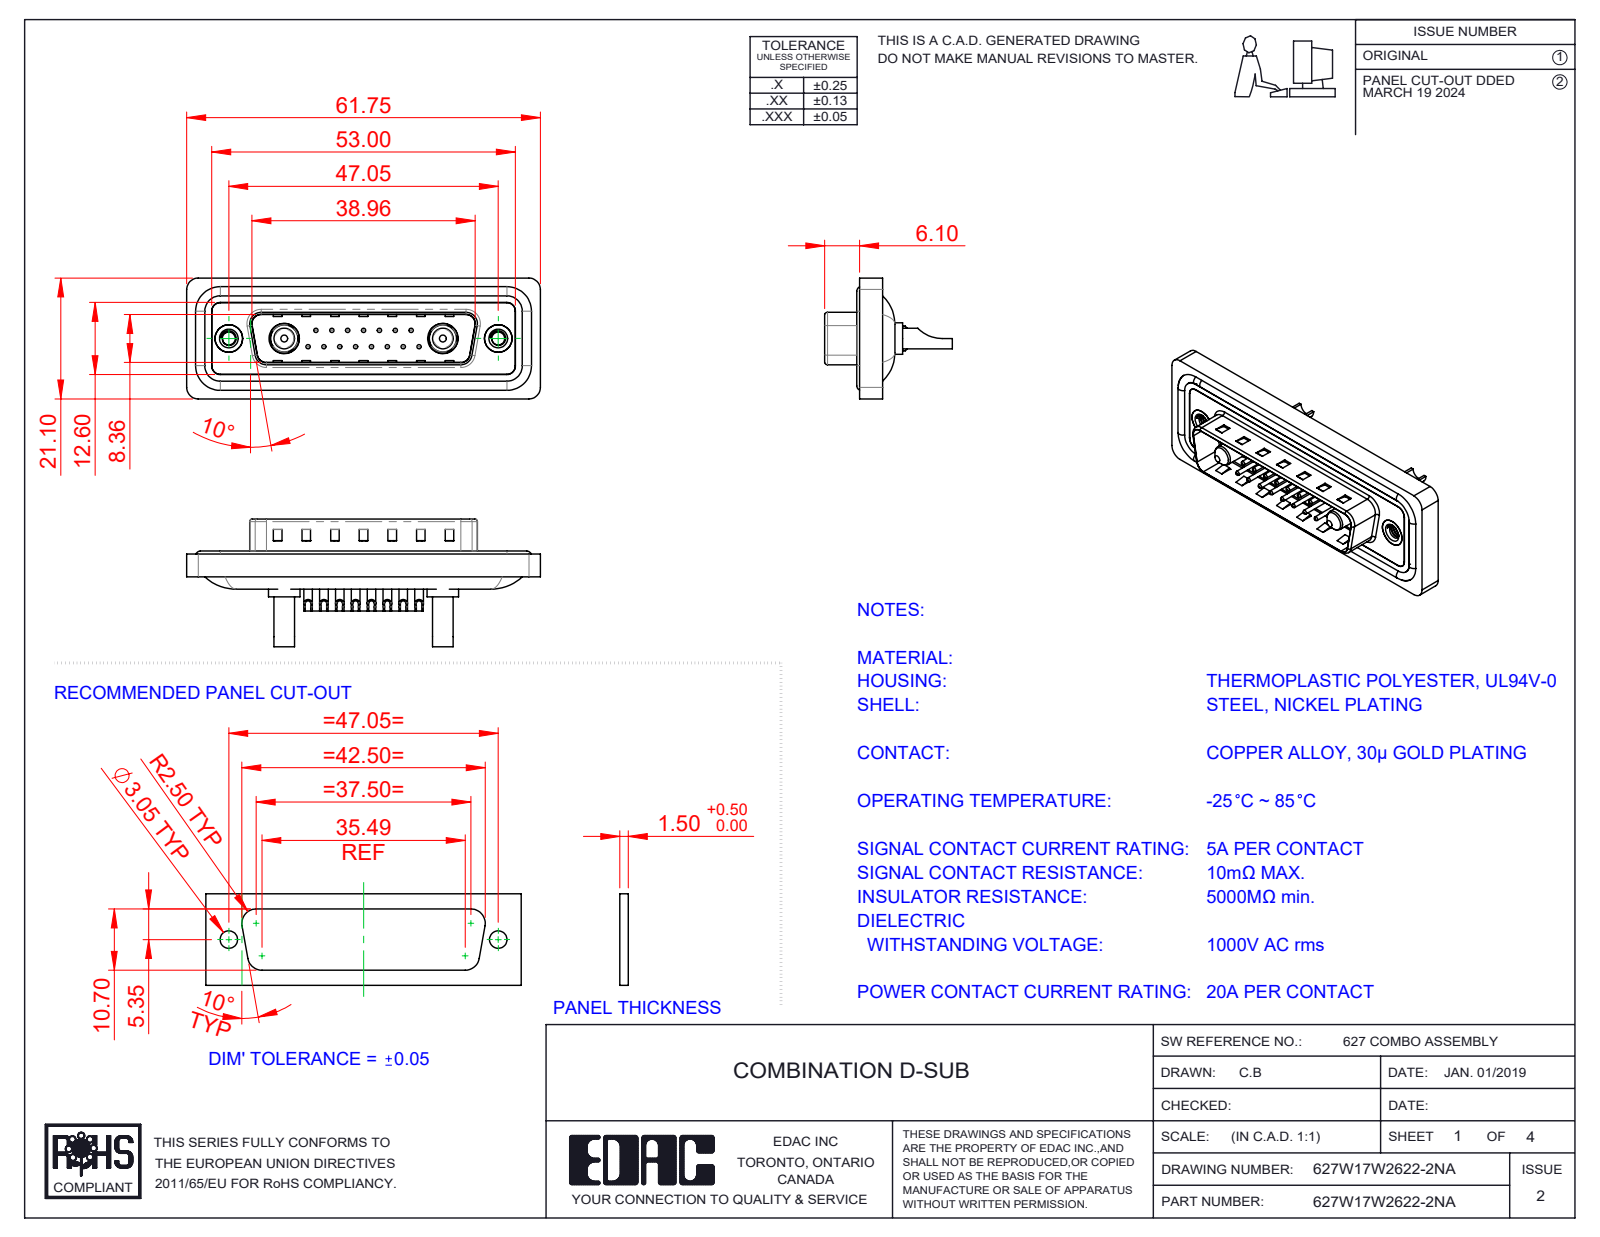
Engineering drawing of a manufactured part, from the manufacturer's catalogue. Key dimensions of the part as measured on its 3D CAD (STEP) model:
Part name (STEP PRODUCT): Power Pin_20A SC; 627Combo Housing_17W2; 627Combo Shell Front_25 Contacts; 627Combo Threaded Rivet_A (+5 more)
STEP written by: SolidWorks 2023 (CONFIG_CONTROL_DESIGN)
Units: millimetres
Bodies: 26 solids, 1128 faces (370 planar, 474 cylindrical, 284 other)
Overall size (bounding box): 61.75 × 22.3 × 21.1
Volume: 7 317 mm³ · Surface area: 12 196 mm²
Round holes (diameter × count): ⌀0.75 ×15, ⌀1 ×15, ⌀1.6 ×15, ⌀2 ×15, ⌀2.26 ×2, ⌀2.7 ×2, ⌀4 ×2, ⌀4.8 ×2, ⌀4.85 ×2, ⌀5 ×2, ⌀5.3 ×2
Round bosses / shafts (diameter × count): ⌀1.5 ×15, ⌀1.6 ×4, ⌀5.5 ×2, ⌀5.2 ×2, ⌀4.9 ×2, ⌀4.75 ×2, ⌀3.75 ×2, ⌀3.6 ×2
Partial cylindrical surfaces — rounded edges, fillets, slot ends (radius × count): R1.5 ×22, R2 ×18, R0.5 ×8, R1.6 ×8, R1 ×6, R0.25 ×4, R0.6 ×4, R0.65 ×4
Main face-to-face distances: 0.4, 1.5, 1.1, 1.6, 0.5, 3.1, 2.9, 0.82, 9.58, 4.1
Hole centre spacings: 3.16, 2.77, 5.54, 8.31, 5.04, 7.49, 11.08, 5.03
